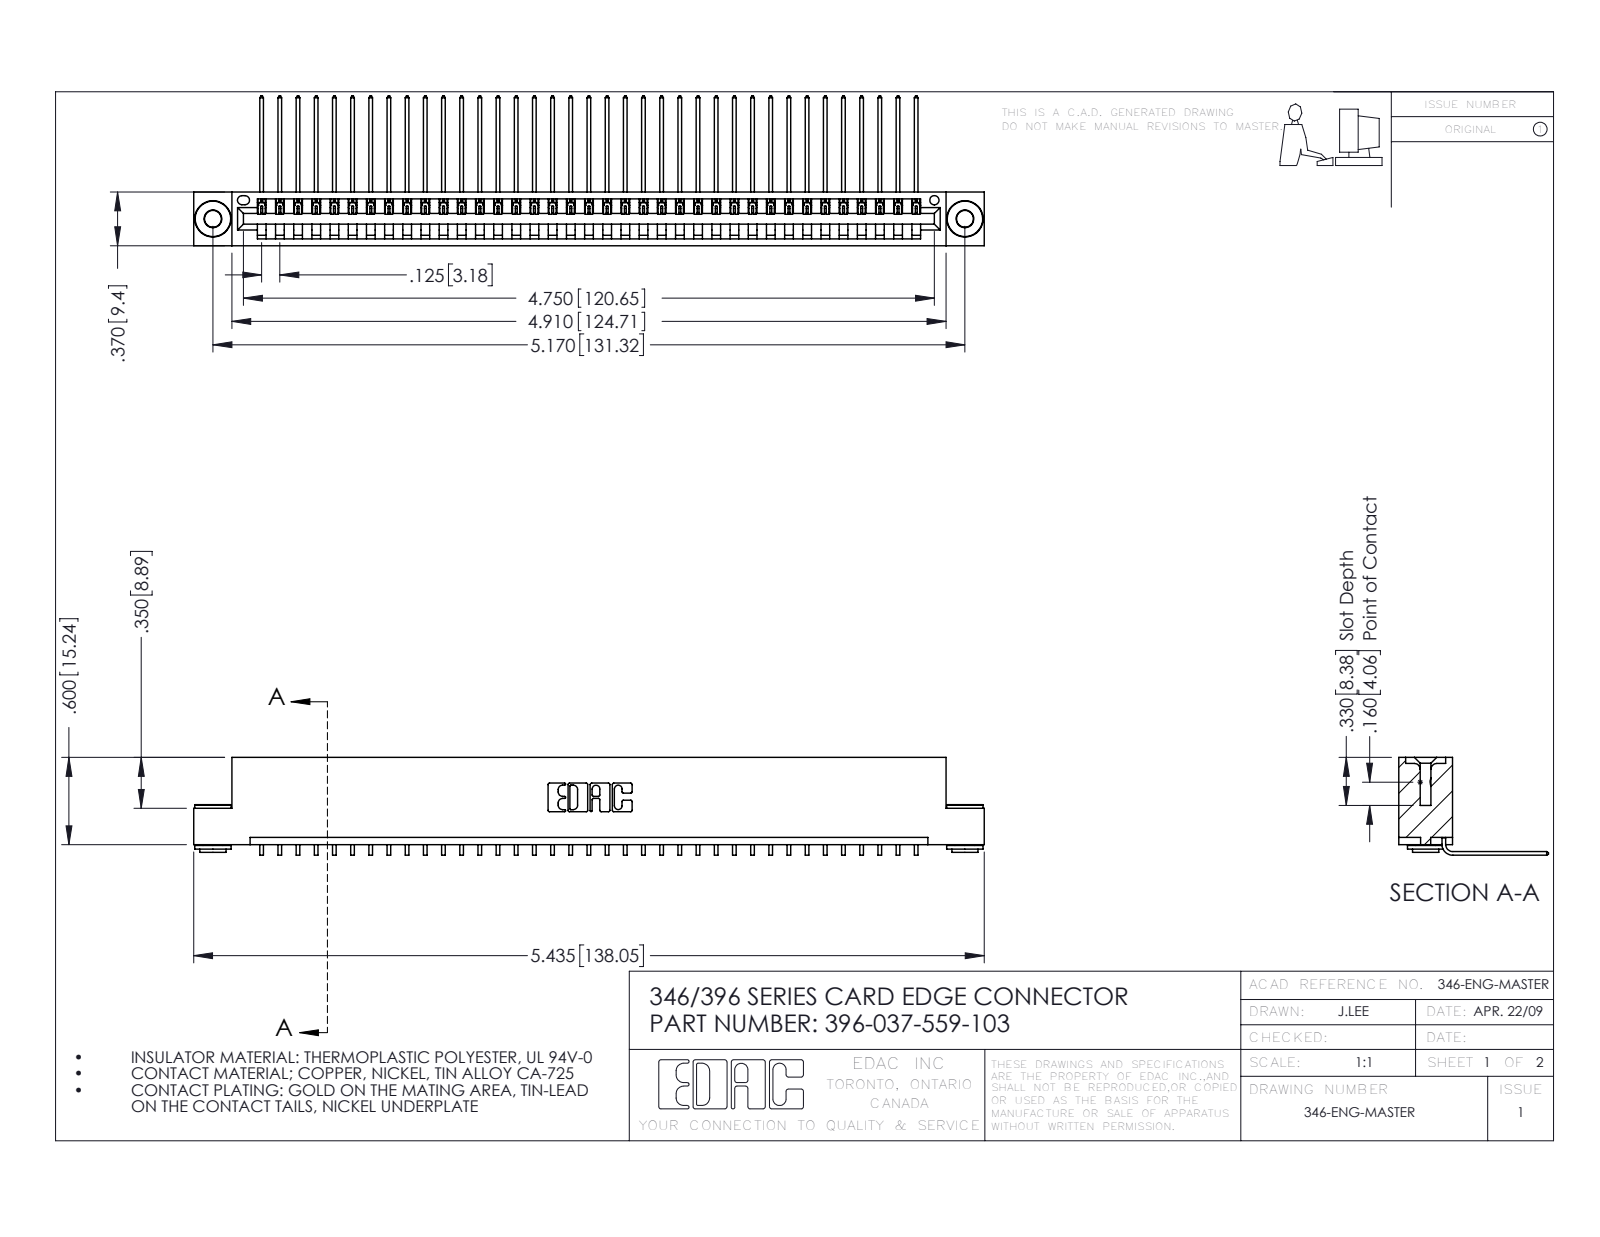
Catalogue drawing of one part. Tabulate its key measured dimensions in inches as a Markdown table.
| quantity | value |
| --- | --- |
| part name | 396-037-559-103; 345-250-002_345-250-002-102; 345-292-001_558 559 Tail - 1; 346 Part_Flush Mounting Lugs - 0.156 Dia-TH |
| STEP written by | SolidWorks 2016 (CONFIG_CONTROL_DESIGN) |
| units | inches |
| bodies | 40 solids, 2380 faces (1640 planar, 732 cylindrical, 8 other) |
| overall size | 5.435 × 1.03 × 0.673 |
| volume | 0.813 in³ |
| surface area | 27.21 in² |
| round holes (diameter × count) | 0.116 × 2, 0.156 × 2, 0.064 × 1 |
| round bosses / shafts (diameter × count) | 0.25 × 2, 0.18 × 2, 0.136 × 2 |
| partial cylindrical surfaces (radius × count) | 0.006 × 74, 0.01 × 22, 0.007 × 6, 0.031 × 6, 0.026 × 3, 0.031 × 2, 0.04 × 2, 0.014 × 1 |
| main face-to-face distances | 0.048, 0.322, 0.37, 0.25, 0.025, 0.072, 0.298, 0.148, 0.222, 0.1 |
| hole center spacings | 0.246, 4.961, 5.17 |
